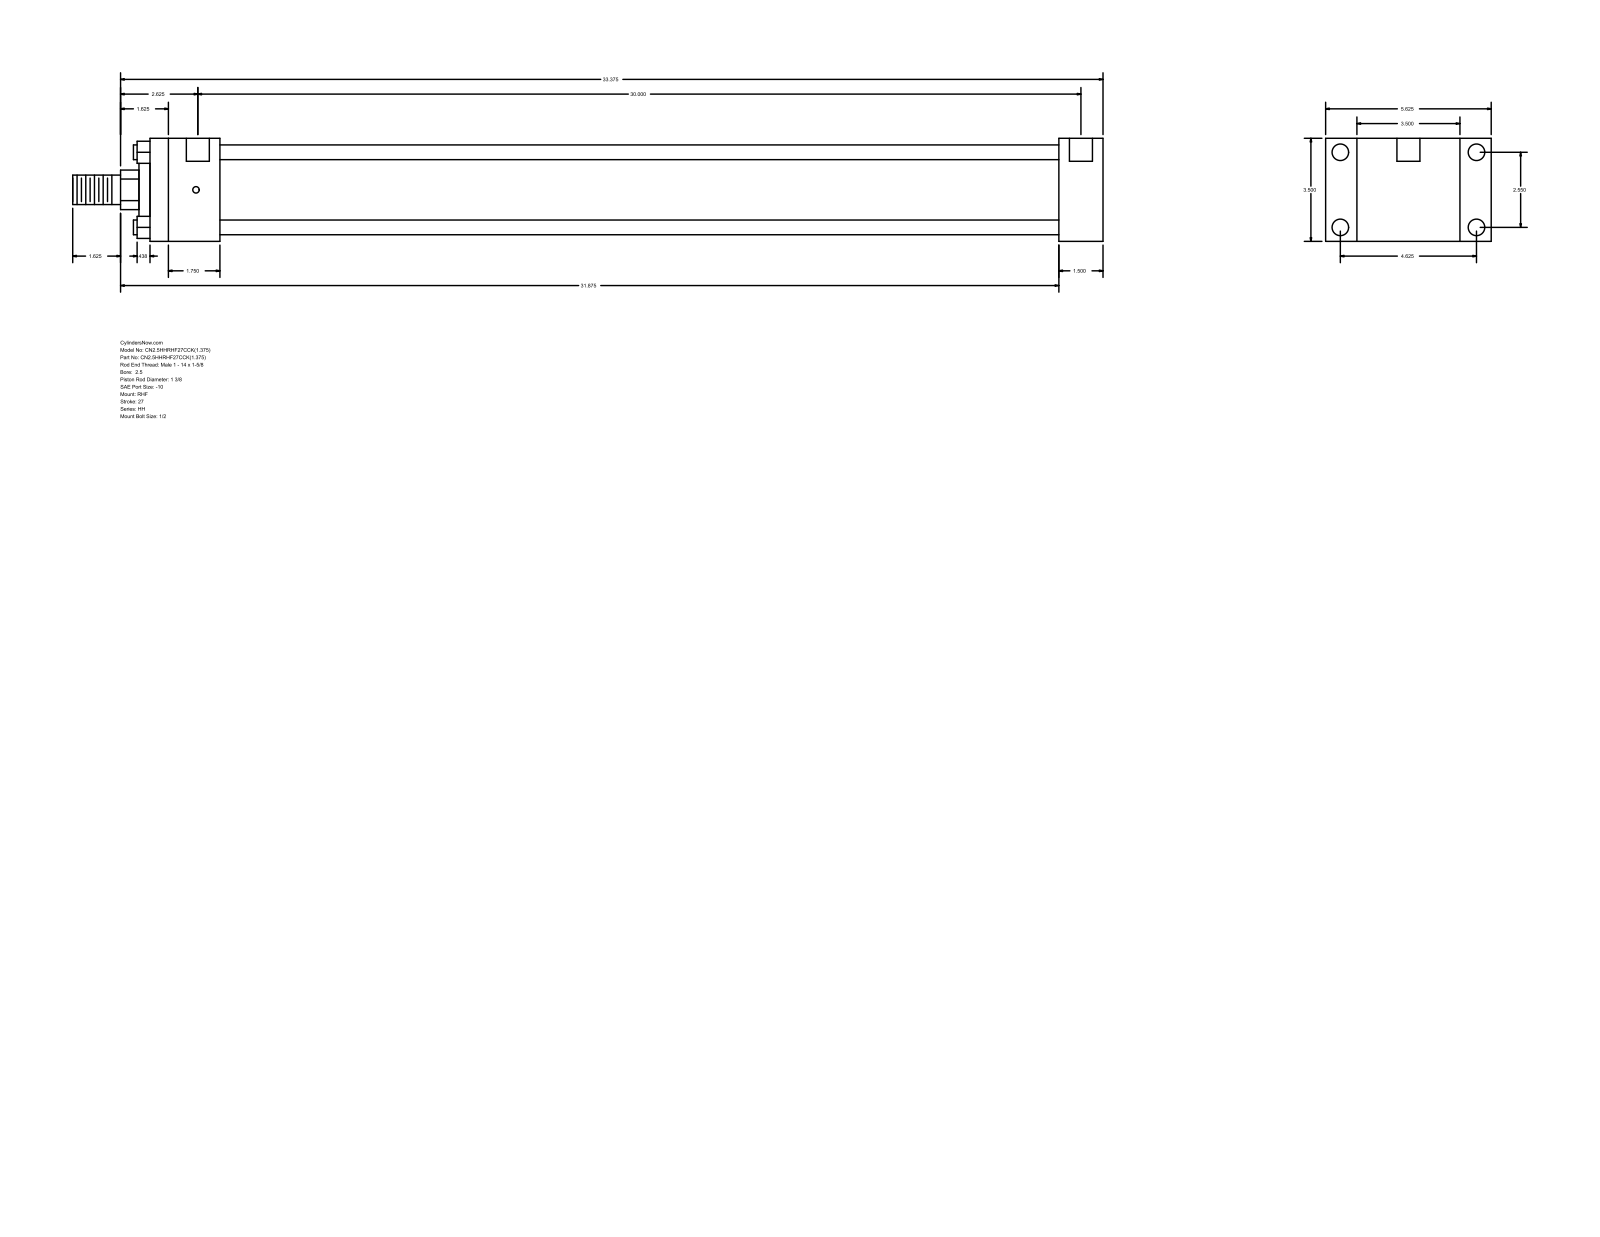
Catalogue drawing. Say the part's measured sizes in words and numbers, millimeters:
The part is named "HH_RHF__0250_1.375". Its 3-D file was written by "GSSL Pune (CONFIG_CONTROL_DESIGN)". It is 0 solids with 88 faces: 60 planar, 28 cylindrical and 0 other. Overall it measures 889 by 142.88 by 88.9 millimeters. Round holes: 4 of diameter 5.56, 4 of diameter 14.3, 2 of diameter 19.84. Round bosses or shafts: 4 of diameter 12.7, 1 of diameter 73.03, 1 of diameter 50.8, 1 of diameter 34.92, 1 of diameter 25.4. Partial cylindrical surfaces (rounded edges, fillets, slot ends): 1 of radius 17.06. The main face-to-face distances are 88.9, 38.11, 26.99, 115.89, 784.22, 822.33, 142.88, 60.32, 723.9, 762.01. The hole center spacings are 64.76, 117.48, 134.15, 765.17, 1.58, 1.59, 762, 763.58.
